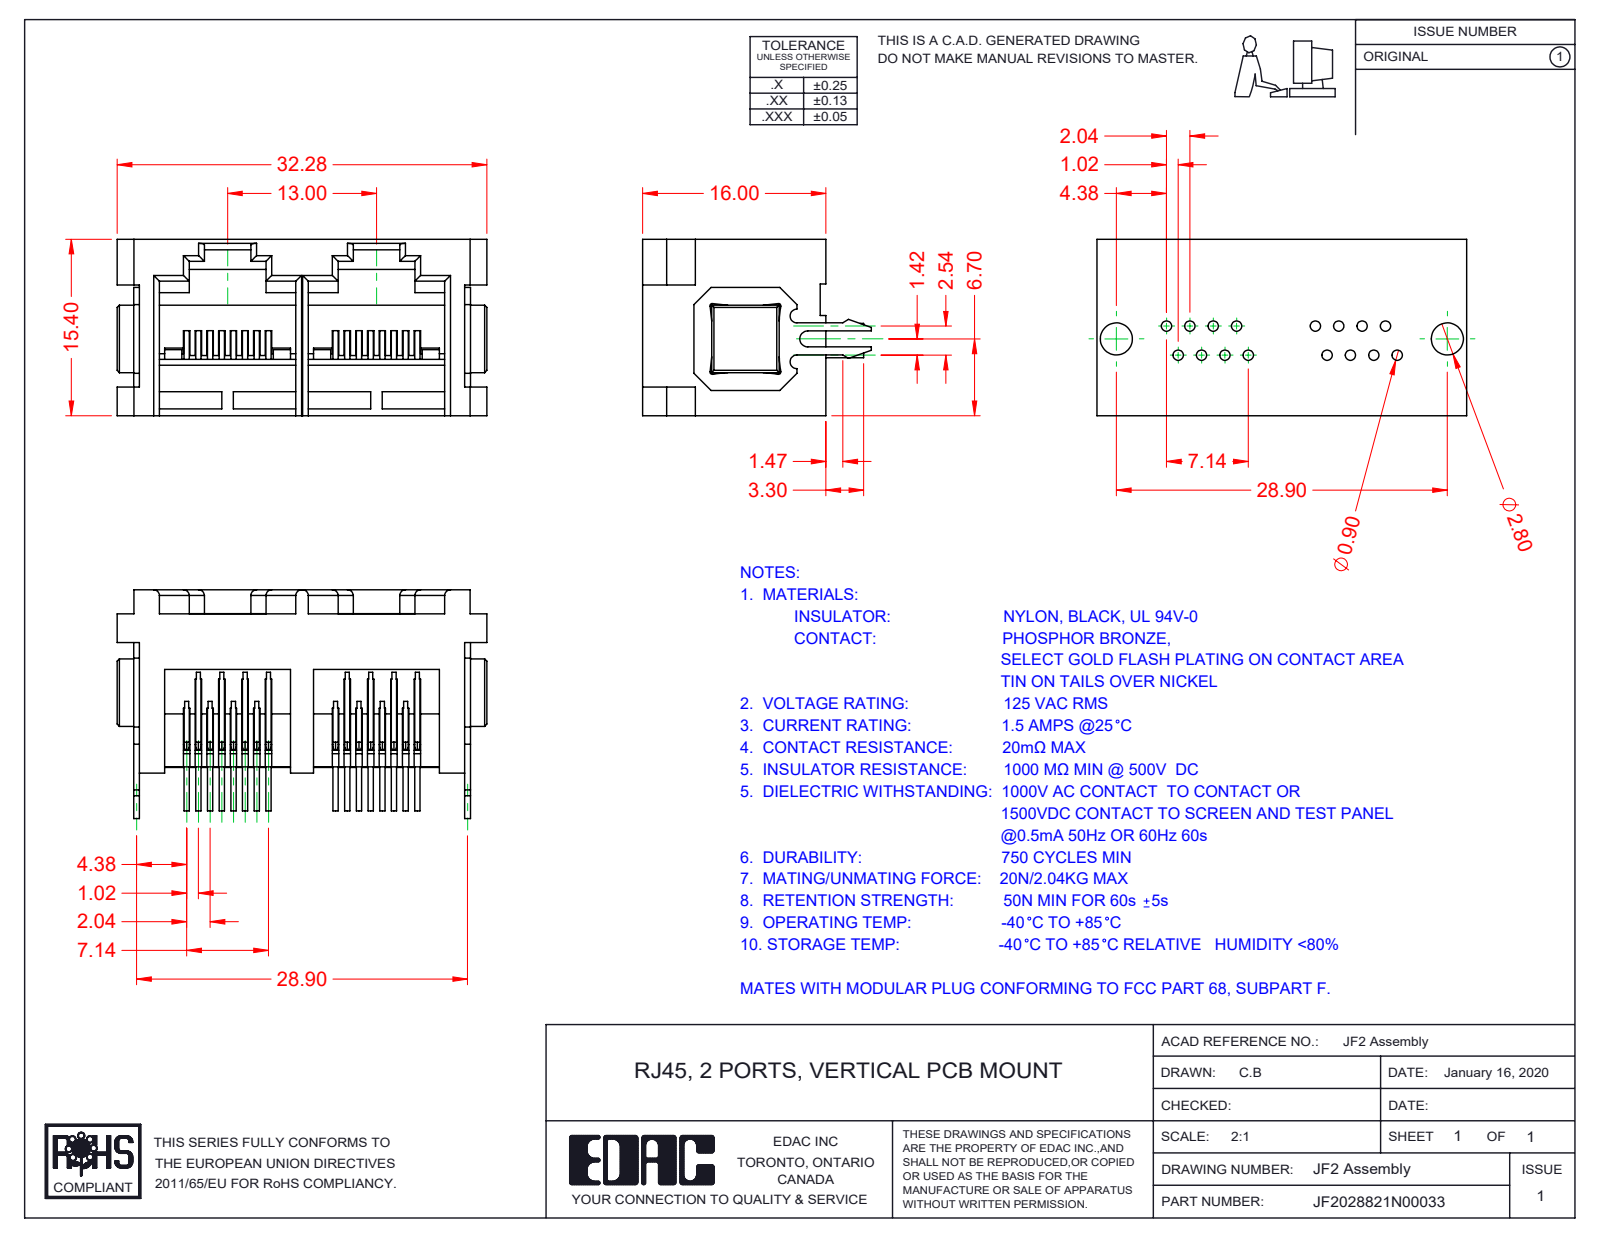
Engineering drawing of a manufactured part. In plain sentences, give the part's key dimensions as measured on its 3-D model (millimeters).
The part is named "F2 Contacts; RJF2028821N00033; F2 Insulator; F2 Boardlocks (+1 more)". Its 3-D file was written by "SolidWorks 2016 (CONFIG_CONTROL_DESIGN)". It is 21 solids with 1130 faces: 734 planar, 300 cylindrical and 96 other. Overall it measures 32.28 by 19.97 by 15.4 millimeters. Its volume is 3 519 cubic millimeters and its surface area 6 910 square millimeters. Round bosses or shafts: 64 of diameter 0.46. Partial cylindrical surfaces (rounded edges, fillets, slot ends): 32 of radius 0.18, 15 of radius 0.5, 4 of radius 0.2, 4 of radius 20.35, 3 of radius 0.3, 2 of radius 0.6, 1 of radius 0.21, 1 of radius 0.45. The main face-to-face distances are 12.59, 2.1, 13, 1.5, 2.81, 0.92, 11.67, 0.5, 28.4, 11.
